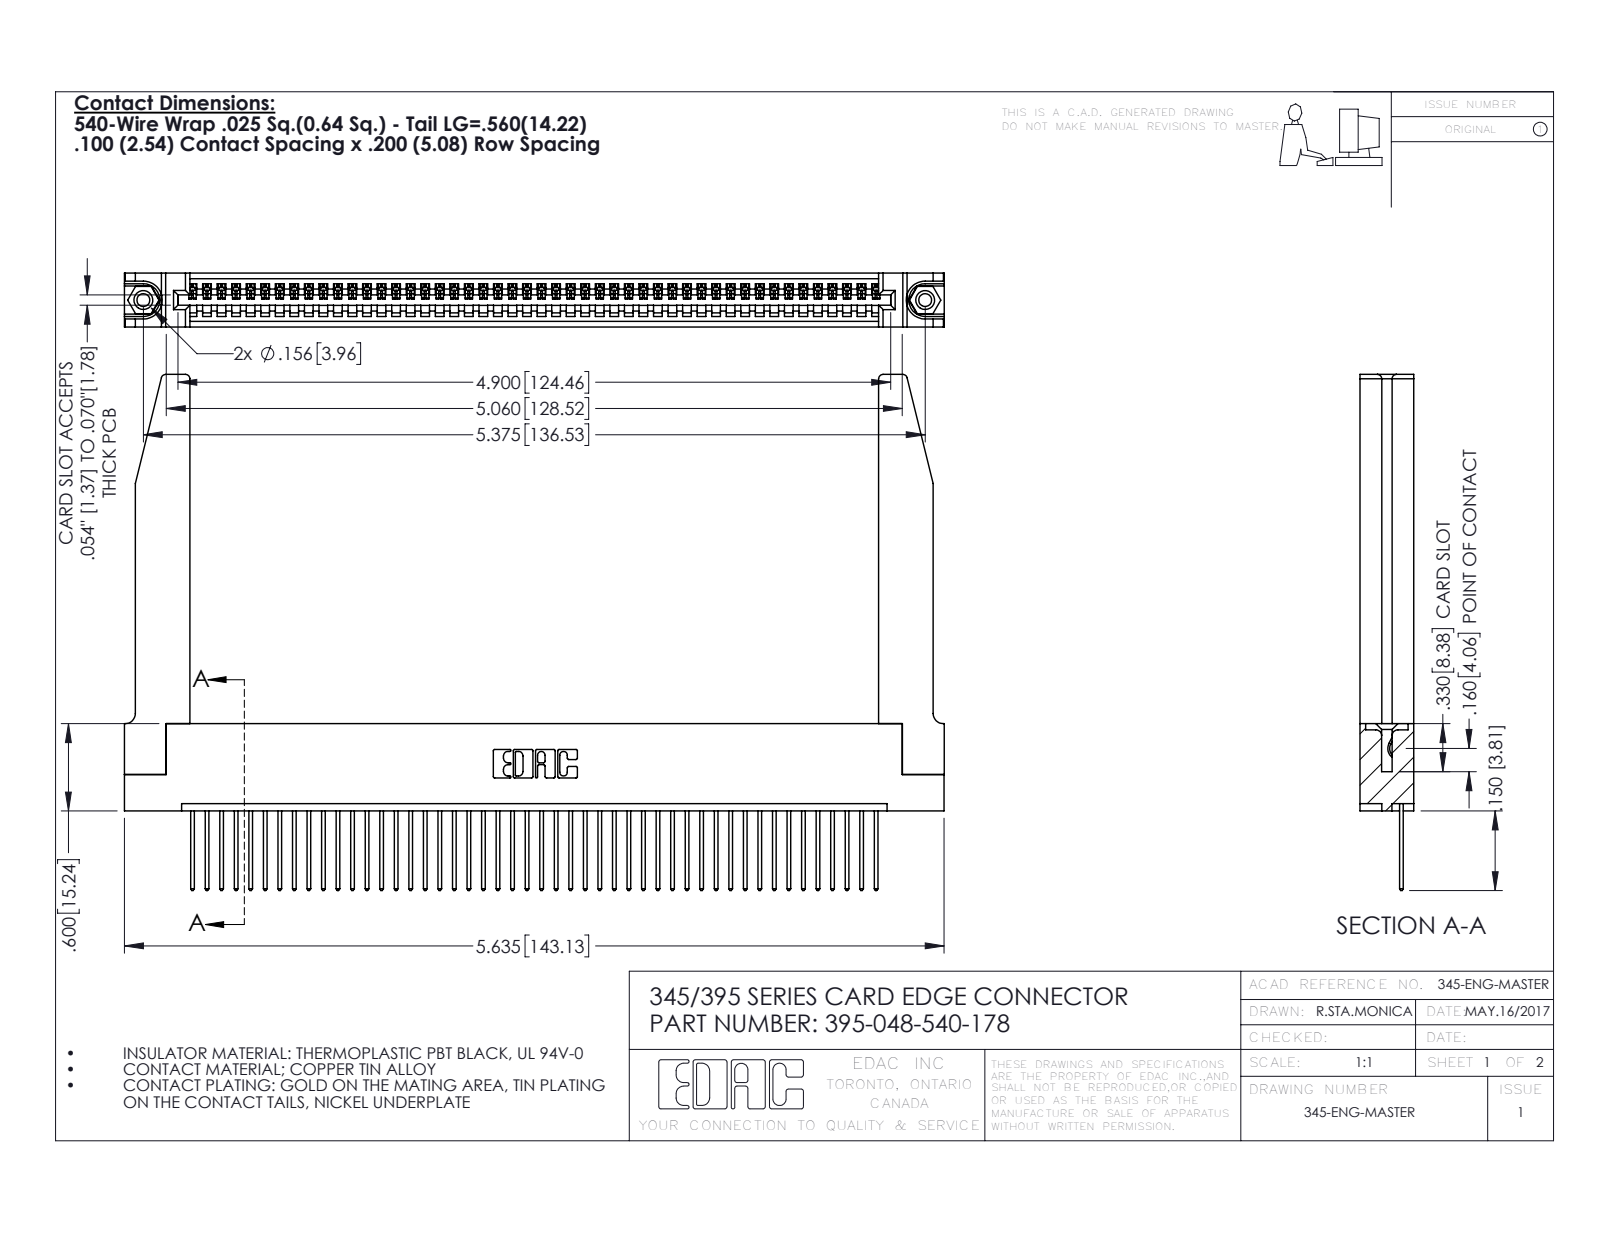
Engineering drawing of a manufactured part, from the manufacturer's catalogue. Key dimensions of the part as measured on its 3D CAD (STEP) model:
Part name (STEP PRODUCT): 395-048-540-178; 345-220-078_345-220-078; 345-250-001_345-250-001-102; 345-292-001_345-293-140 (+1 more)
STEP written by: SolidWorks 2016 (CONFIG_CONTROL_DESIGN)
Units: inches
Bodies: 53 solids, 3144 faces (2142 planar, 950 cylindrical, 52 other)
Overall size (bounding box): 5.636 × 3.547 × 0.37
Volume: 1.311 in³ · Surface area: 39.7 in²
Round holes (diameter × count): ⌀0.089 ×2, ⌀0.125 ×2, ⌀0.156 ×2, ⌀0.064 ×1
Round bosses / shafts (diameter × count): ⌀0.155 ×2
Partial cylindrical surfaces — rounded edges, fillets, slot ends (radius × count): R0.006 ×96, R0.01 ×96, R0.01 ×22, R0.03 ×8, R0.007 ×6, R0.031 ×6, R0.026 ×3, R0.031 ×2
Main face-to-face distances: 0.072, 0.37, 0.298, 0.098, 0.272, 0.025, 0.2, 0.225, 0.15, 0.148
Hole centre spacings: 0.27, 5.139, 5.375
